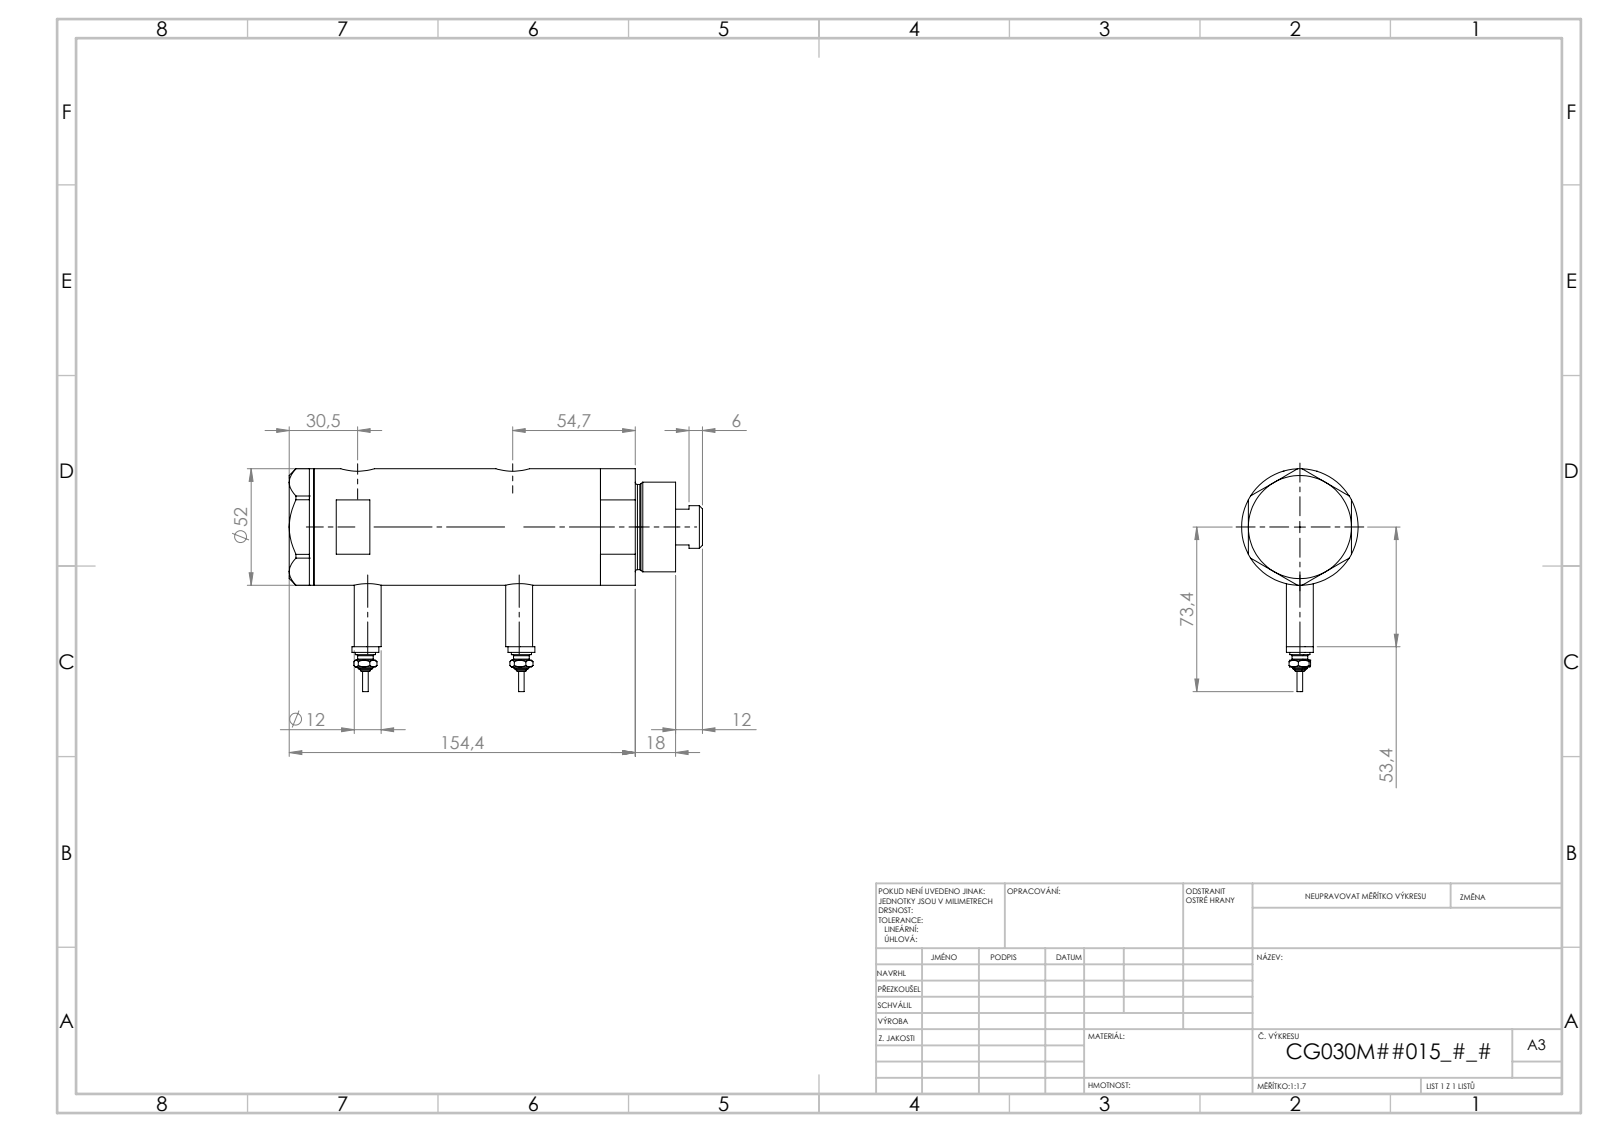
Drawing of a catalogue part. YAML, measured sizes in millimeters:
part_name: "Switch; V270CG_VC; V270CG_BACK; V270CG_FRONT (+1 more)"
step_written_by: "SolidWorks 2019 (CONFIG_CONTROL_DESIGN)"
units: millimeters
bodies: {solids: 6, faces: 226, planar: 93, cylindrical: 69, other: 64}
overall_size: [184.4, 99.4, 52]
volume: 346825
surface_area: 80384
round_holes:
  - {diameter: 9.73, count: 2}
  - {diameter: 12.5, count: 2}
  - {diameter: 15, count: 2}
  - {diameter: 6.5, count: 1}
  - {diameter: 20, count: 1}
  - {diameter: 21.5, count: 1}
  - {diameter: 30, count: 1}
  - {diameter: 33, count: 1}
  - {diameter: 44, count: 1}
round_bosses_or_shafts:
  - {diameter: 12, count: 4}
  - {diameter: 9, count: 2}
  - {diameter: 7, count: 2}
  - {diameter: 4.5, count: 2}
  - {diameter: 2.5, count: 2}
  - {diameter: 52, count: 1}
  - {diameter: 40, count: 1}
  - {diameter: 38, count: 1}
face_to_face_distances: [91.5, 23.8, 67.7, 11, 34.8, 102.5, 46, 36.4, 138.9, 127.9]
hole_center_spacings: [2.9, 4.5, 64.7, 67.6, 69.2, 72.1]
